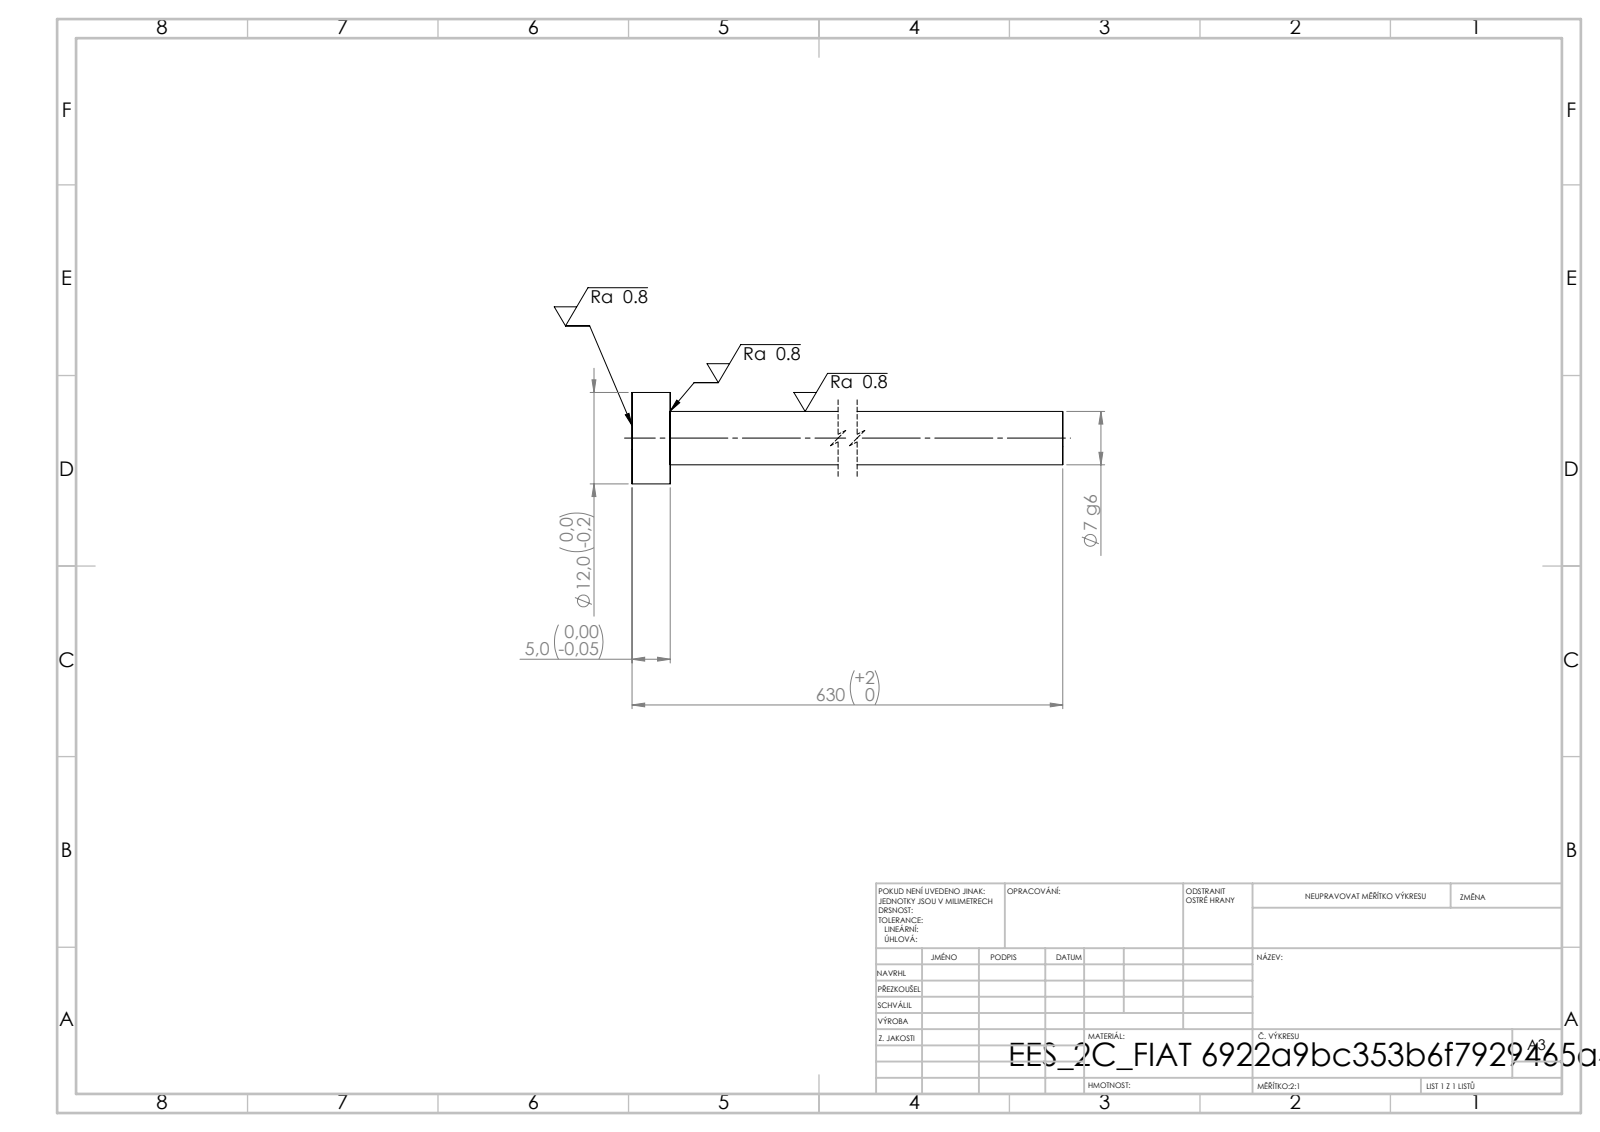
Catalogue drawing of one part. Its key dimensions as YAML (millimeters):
step_written_by: "SolidWorks 2019 (CONFIG_CONTROL_DESIGN)"
units: millimeters
bodies: {solids: 1, faces: 7, planar: 3, cylindrical: 4, other: 0}
overall_size: [630, 12, 12]
volume: 24618
surface_area: 14159
round_bosses_or_shafts:
  - {diameter: 12, count: 1}
  - {diameter: 7, count: 1}
face_to_face_distances: [5, 630, 625]
